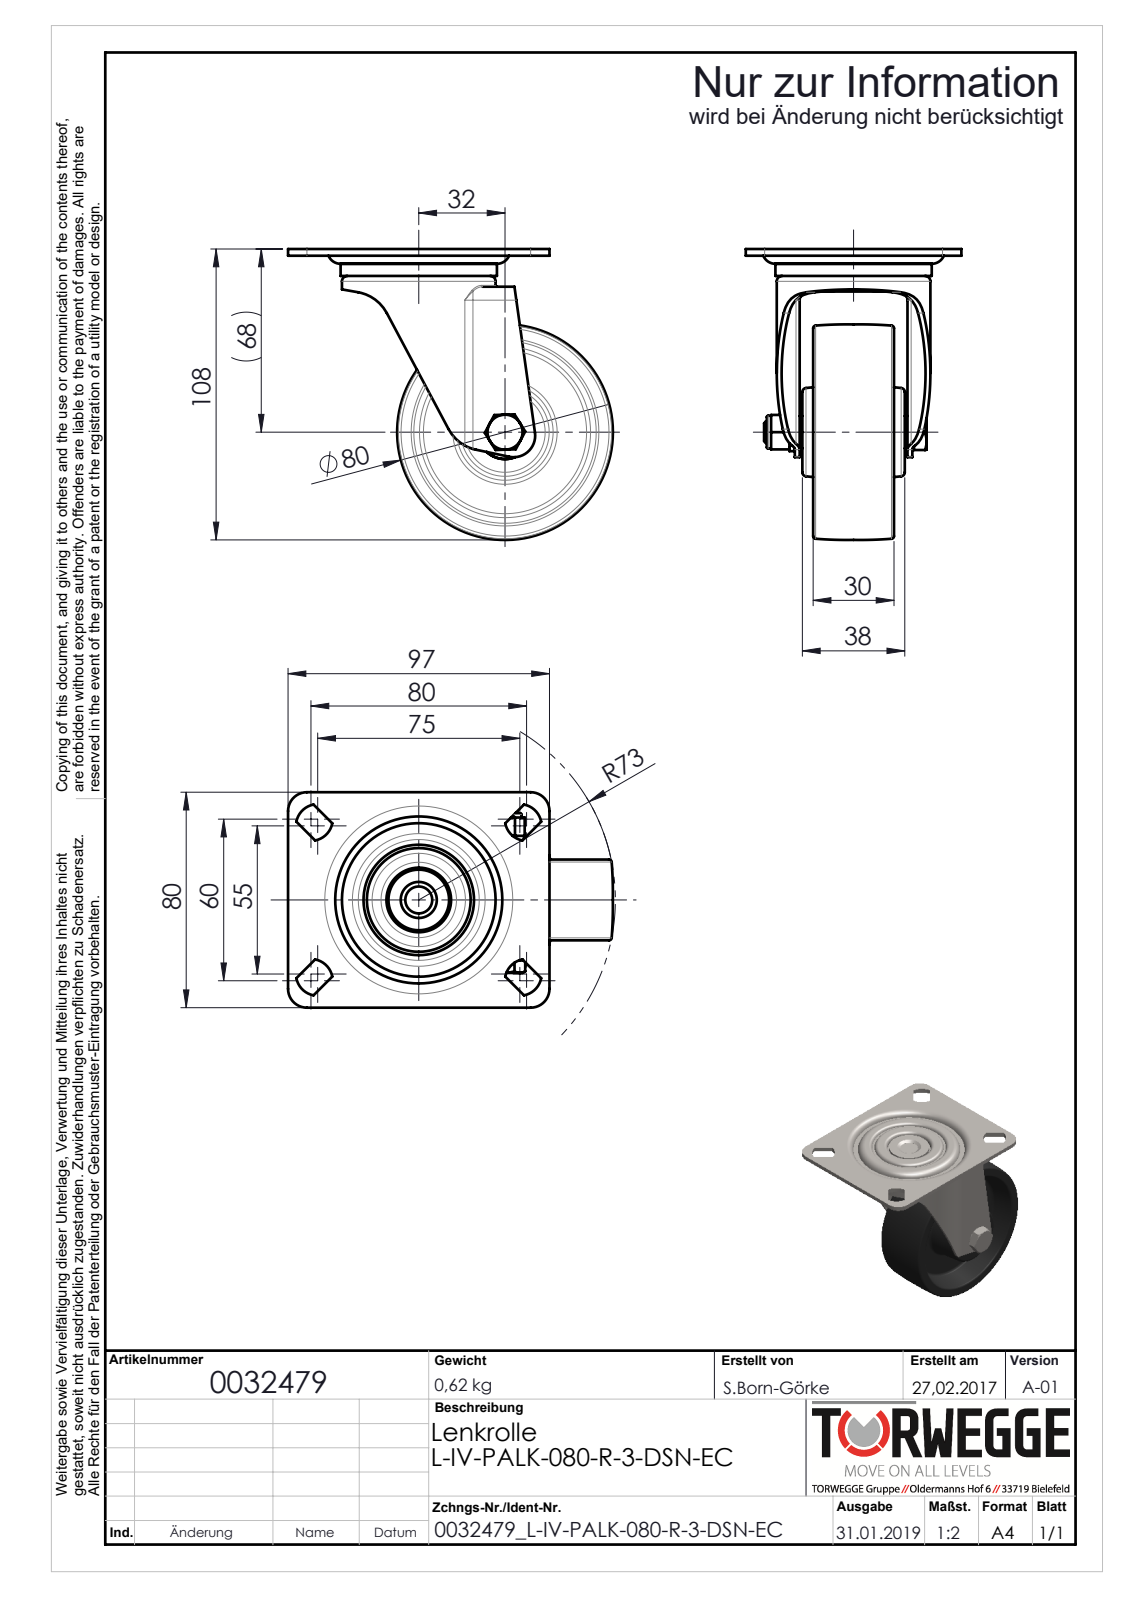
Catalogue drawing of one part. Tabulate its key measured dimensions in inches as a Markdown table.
| quantity | value |
| --- | --- |
| part name | 0032479_L-IV-PALK-080-R-3-DSN-EC_(A-01) |
| STEP written by | SolidWorks 2018 (AUTOMOTIVE_DESIGN) |
| units | inches |
| bodies | 9 solids, 227 faces (77 planar, 66 cylindrical, 84 other) |
| overall size | 4.745 × 4.253 × 3.15 |
| volume | 8.765 in³ |
| surface area | 107.8 in² |
| round holes (diameter × count) | 0.262 × 1, 0.319 × 1, 0.327 × 1, 0.354 × 1, 0.394 × 1, 0.48 × 1, 0.945 × 1, 2.102 × 1 |
| round bosses / shafts (diameter × count) | 2.283 × 1, 2.244 × 1, 0.886 × 1, 0.787 × 1, 0.555 × 1, 0.512 × 1, 0.472 × 1, 0.315 × 1 |
| partial cylindrical surfaces (radius × count) | 0.318 × 8, 0.197 × 4, 0.276 × 4, 0.126 × 2, 0.268 × 2, 0.591 × 2, 0.315 × 1 |
| main face-to-face distances | 0.689, 0.098, 0.118, 0.217, 0.197, 0.071, 0.76, 0.957, 0.492, 0.248 |
